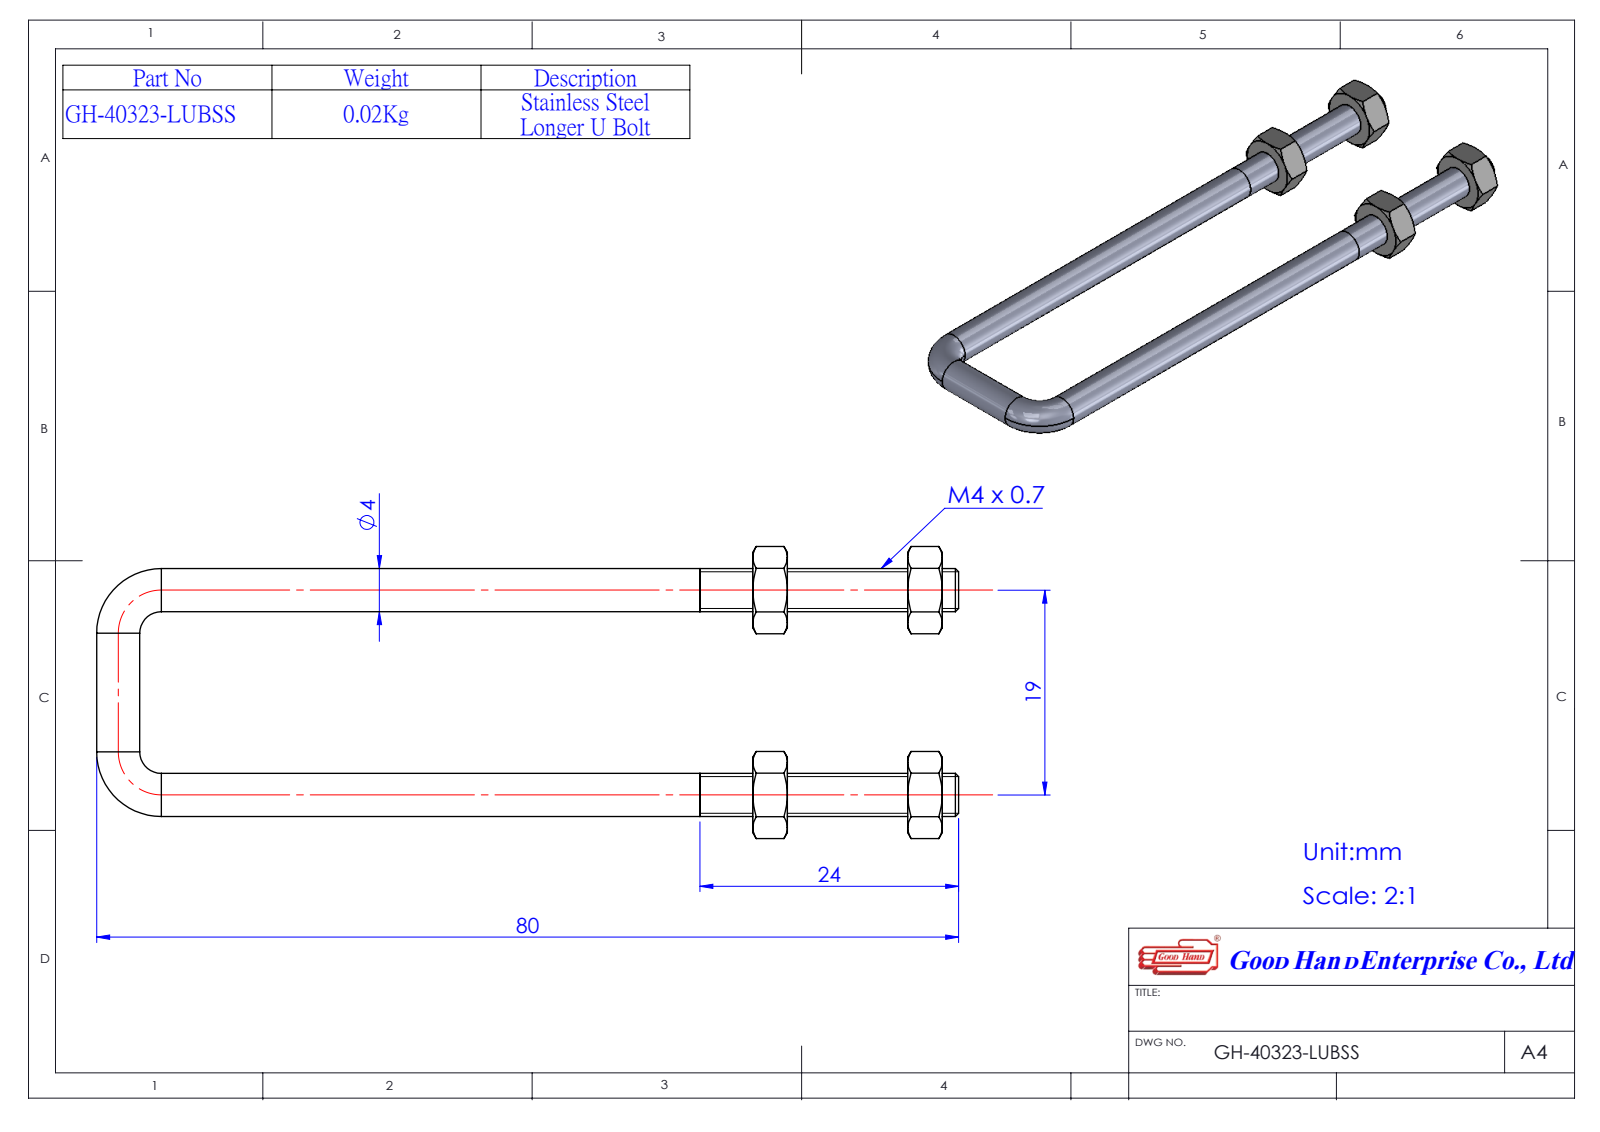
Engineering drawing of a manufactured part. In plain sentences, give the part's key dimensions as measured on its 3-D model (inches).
The part is named "GH-40323-LUBSS". Its 3-D file was written by "SolidWorks 2016 (AUTOMOTIVE_DESIGN)". It is 3 solids with 24 faces: 6 planar, 10 cylindrical and 8 other. Overall it measures 3.15 by 0.906 by 0.157 inches. Its volume is 0.132 cubic inches and its surface area 3.452 square inches. Round bosses or shafts: 3 of diameter 0.157. The main face-to-face distances are 0.945.
